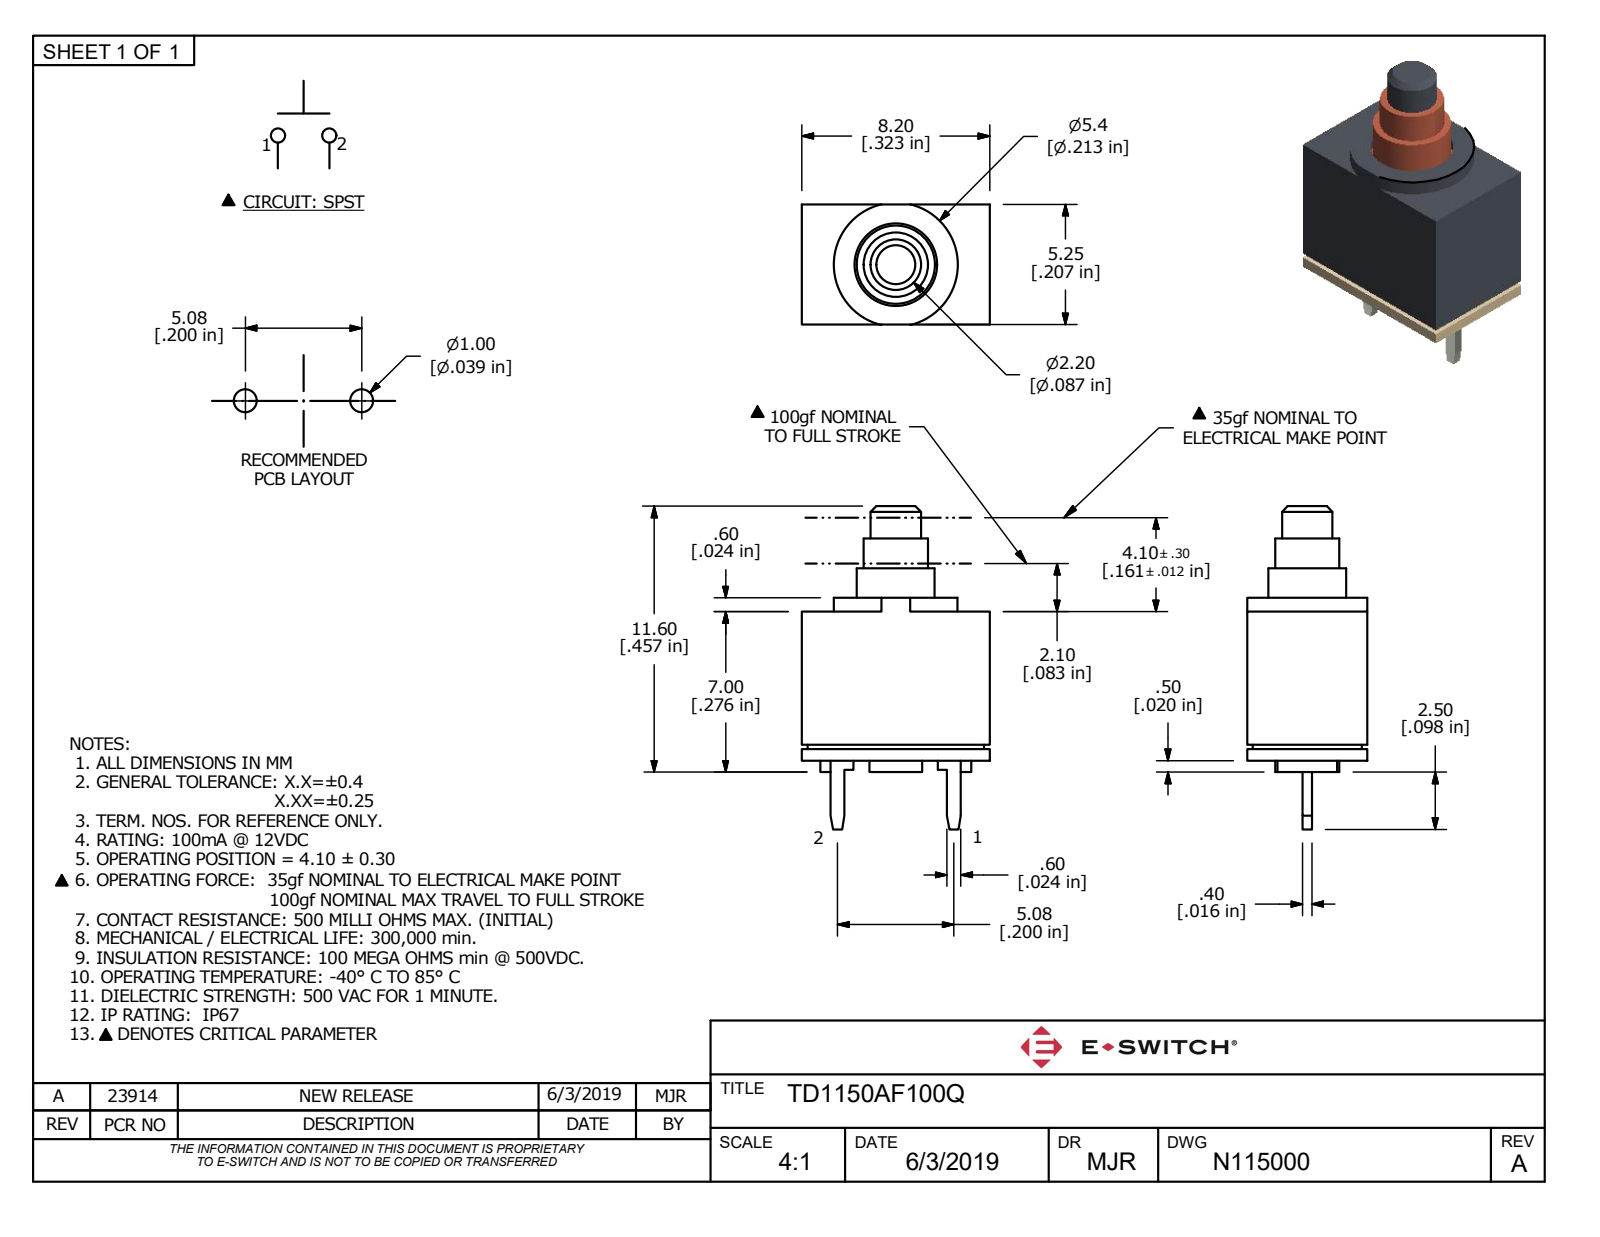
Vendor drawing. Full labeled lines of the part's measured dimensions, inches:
Part name (STEP PRODUCT): TD1150AF100Q
STEP written by: Autodesk Inventor 2018 (AP242_MANAGED_MODEL_BASED_3D_ENGINEERING_MIM_LF)
Units: inches
Bodies: 1 solid, 103 faces (92 planar, 10 cylindrical, 1 other)
Overall size (bounding box): 0.535 × 0.323 × 0.207
Volume: 0.012 in³ · Surface area: 0.936 in²
Round holes (diameter × count): ⌀0.102 ×1, ⌀0.142 ×1
Round bosses / shafts (diameter × count): ⌀0.213 ×1, ⌀0.134 ×1, ⌀0.11 ×1, ⌀0.087 ×1
Partial cylindrical surfaces — rounded edges, fillets, slot ends (radius × count): R0.087 ×1
Main face-to-face distances: 0.179, 0.027, 0.028, 0.02, 0.206, 0.295, 0.152, 0.13, 0.106, 0.323
